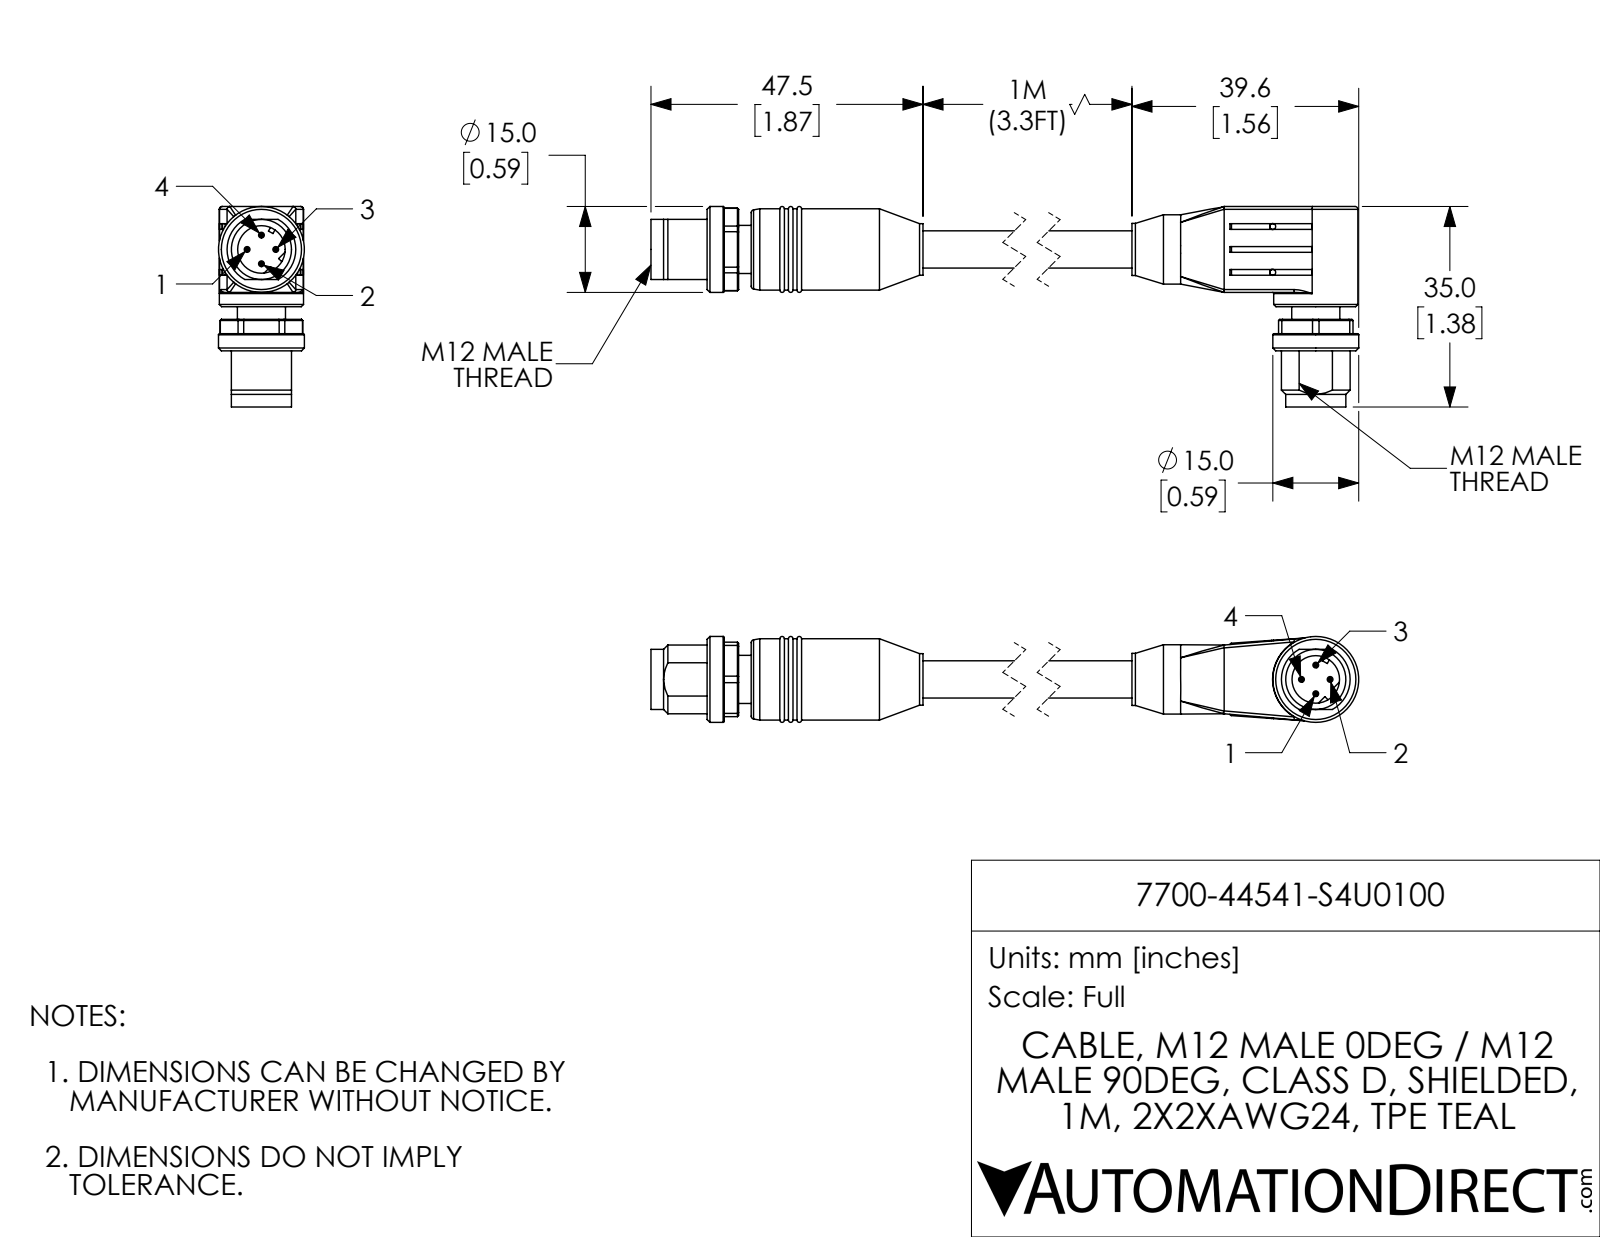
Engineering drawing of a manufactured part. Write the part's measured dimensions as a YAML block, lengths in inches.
part_name: "7700-44541-S4U0100; 7700-44541-S4U0100_MALE90; 7700-44541-S4U0100_MALE"
step_written_by: "SolidWorks 2017 (AUTOMOTIVE_DESIGN)"
units: inches
bodies: {solids: 2, faces: 284, planar: 114, cylindrical: 90, other: 80}
overall_size: [5.476, 1.378, 0.591]
volume: 0.955
surface_area: 10.92
round_holes:
  - {diameter: 0.041, count: 4}
  - {diameter: 0.327, count: 2}
  - {diameter: 0.189, count: 1}
round_bosses_or_shafts:
  - {diameter: 0.039, count: 8}
  - {diameter: 0.591, count: 2}
  - {diameter: 0.413, count: 2}
  - {diameter: 0.331, count: 2}
  - {diameter: 0.579, count: 1}
  - {diameter: 0.559, count: 1}
  - {diameter: 0.476, count: 1}
  - {diameter: 0.358, count: 1}
partial_cylinders:
  - {radius: 0.02, count: 4}
  - {radius: 0.012, count: 2}
  - {radius: 0.236, count: 2}
  - {radius: 0.283, count: 2}
face_to_face_distances: [0.689, 0.087, 0.098, 0.185, 0.591, 0.035, 0.252, 0.339, 0.217, 0.303]
hole_center_spacings: [0.315]
